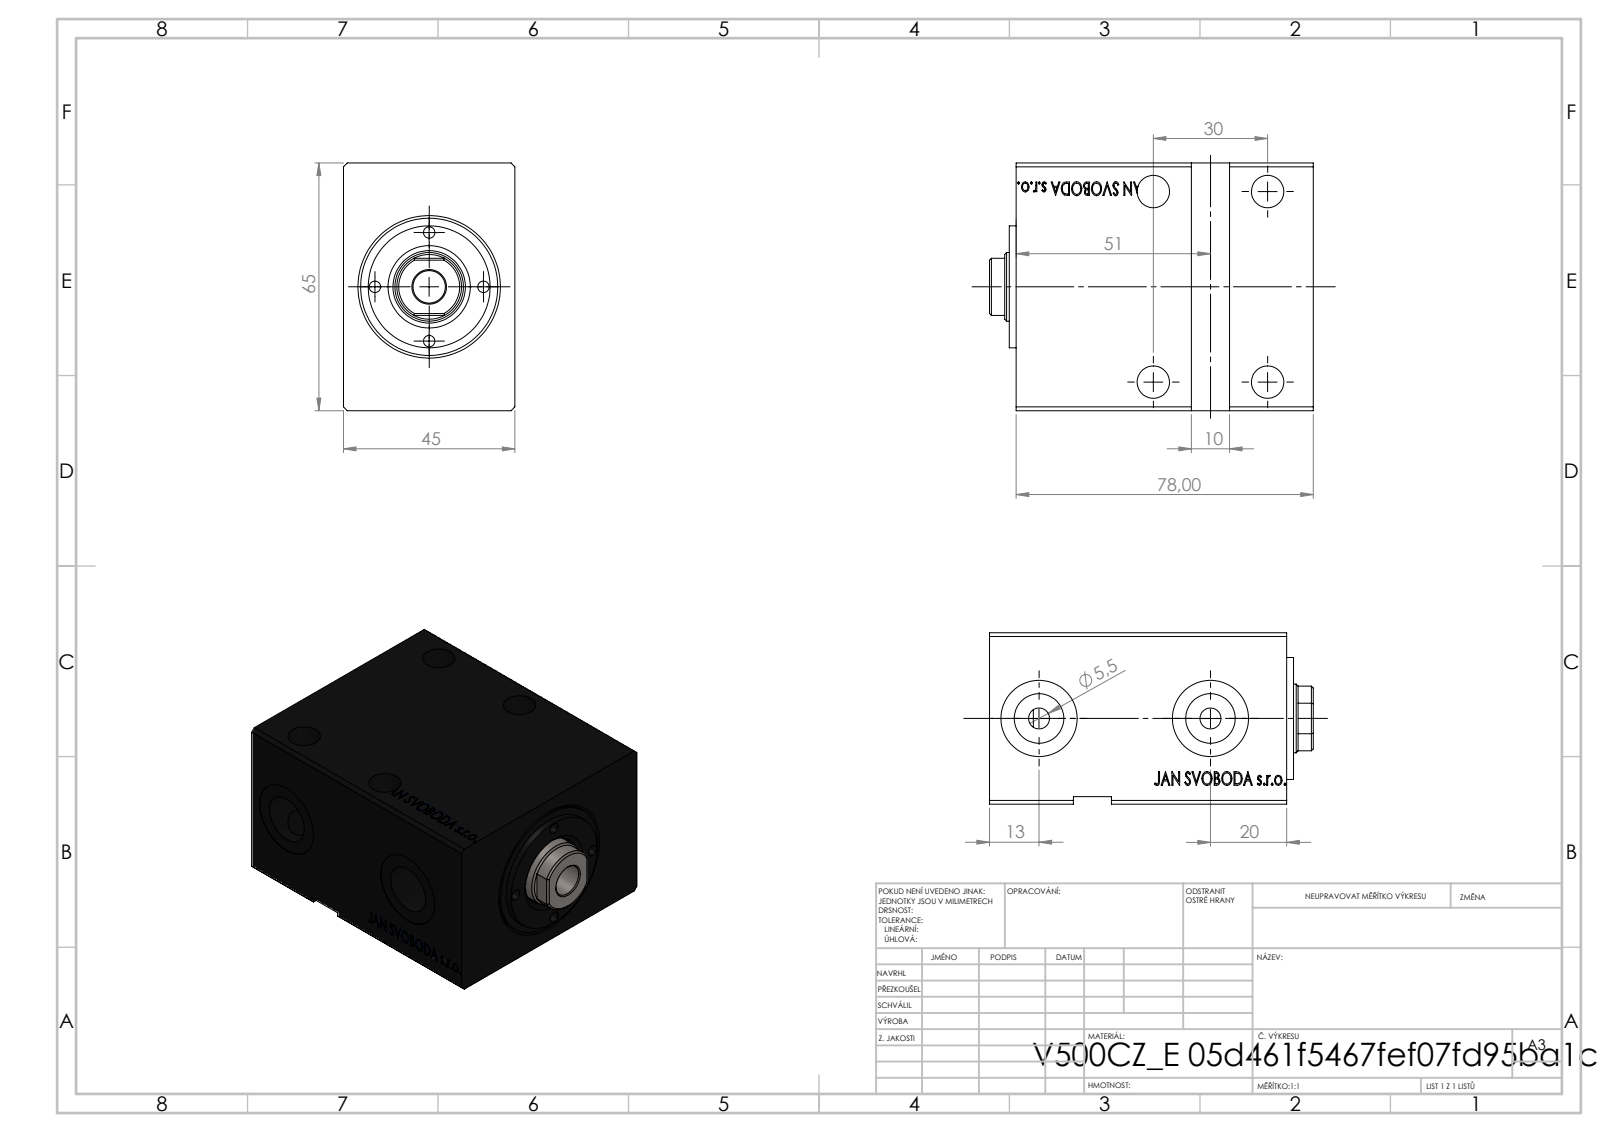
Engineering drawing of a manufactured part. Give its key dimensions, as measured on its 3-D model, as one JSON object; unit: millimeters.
{"step_written_by": "SolidWorks 2019 (CONFIG_CONTROL_DESIGN)", "units": "millimeters", "bodies": {"solids": 1, "faces": 772, "planar": 372, "cylindrical": 28, "other": 372}, "overall_size": [78, 65, 45], "volume_mm3": 149862, "surface_area_mm2": 35495, "round_holes": [[8.5, 4], [5.5, 2], [13, 2], [20, 2], [25, 1], [36, 1]], "face_to_face_distances": [45, 65, 78, 77.8, 2, 43, 58, 19.8, 20, 8.5], "hole_center_spacings": [30, 50, 58.31, 45]}
